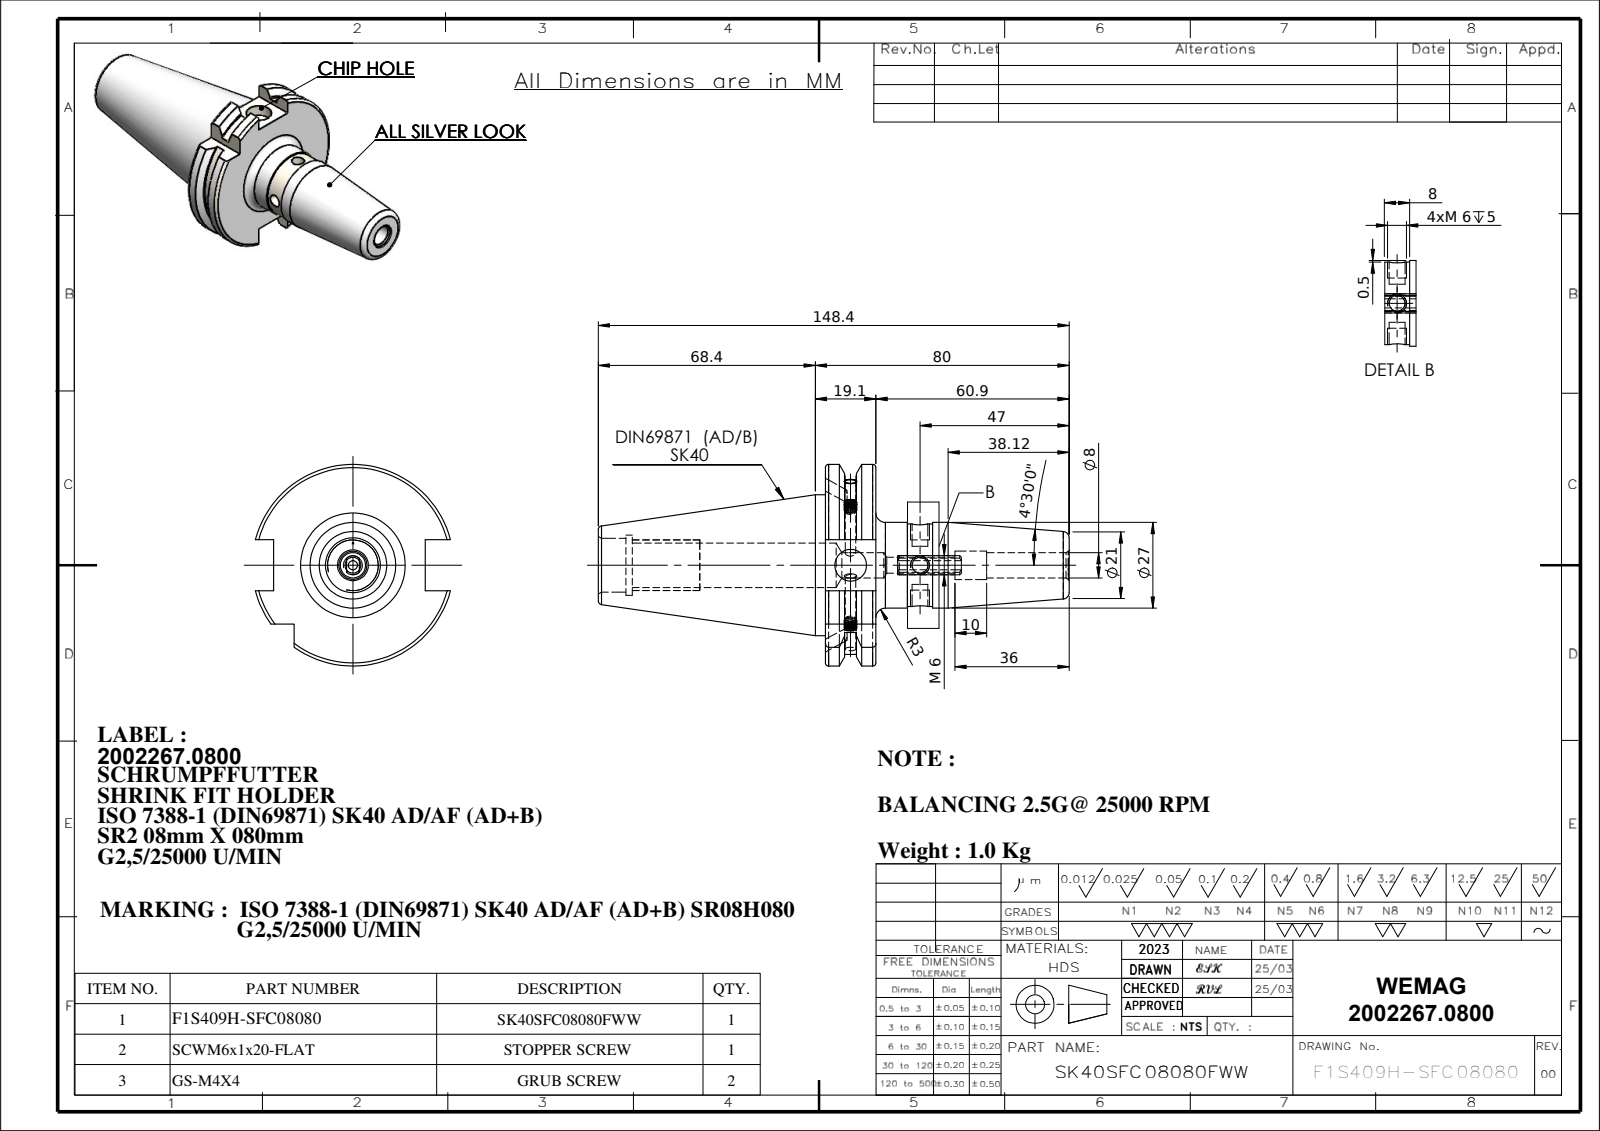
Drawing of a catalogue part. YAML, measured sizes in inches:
part_name: "GS-M4X4_DIN 913 - M4 x 4-N; 91406-SR208080; SK40SFC08080FWW; SCWM6x1x20-FLAT"
step_written_by: "SolidWorks 2018 (CONFIG_CONTROL_DESIGN)"
units: inches
bodies: {solids: 4, faces: 235, planar: 58, cylindrical: 73, other: 104}
overall_size: [5.843, 2.502, 2.42]
volume: 7.746
surface_area: 43.97
round_holes:
  - {diameter: 0.197, count: 3}
  - {diameter: 0.114, count: 1}
  - {diameter: 0.13, count: 1}
  - {diameter: 0.315, count: 1}
  - {diameter: 0.315, count: 1}
  - {diameter: 0.354, count: 1}
  - {diameter: 0.394, count: 1}
  - {diameter: 0.551, count: 1}
  - {diameter: 0.669, count: 1}
  - {diameter: 0.748, count: 1}
round_bosses_or_shafts:
  - {diameter: 0.157, count: 2}
  - {diameter: 1.75, count: 1}
  - {diameter: 1.063, count: 1}
  - {diameter: 1.024, count: 1}
partial_cylinders:
  - {radius: 0.118, count: 1}
  - {radius: 1.107, count: 1}
  - {radius: 1.251, count: 1}
face_to_face_distances: [0.626, 2.398, 3.024, 0.634, 1.882, 0.157, 2.819, 3.445, 5.843, 0.421]
hole_center_spacings: [0.86]
